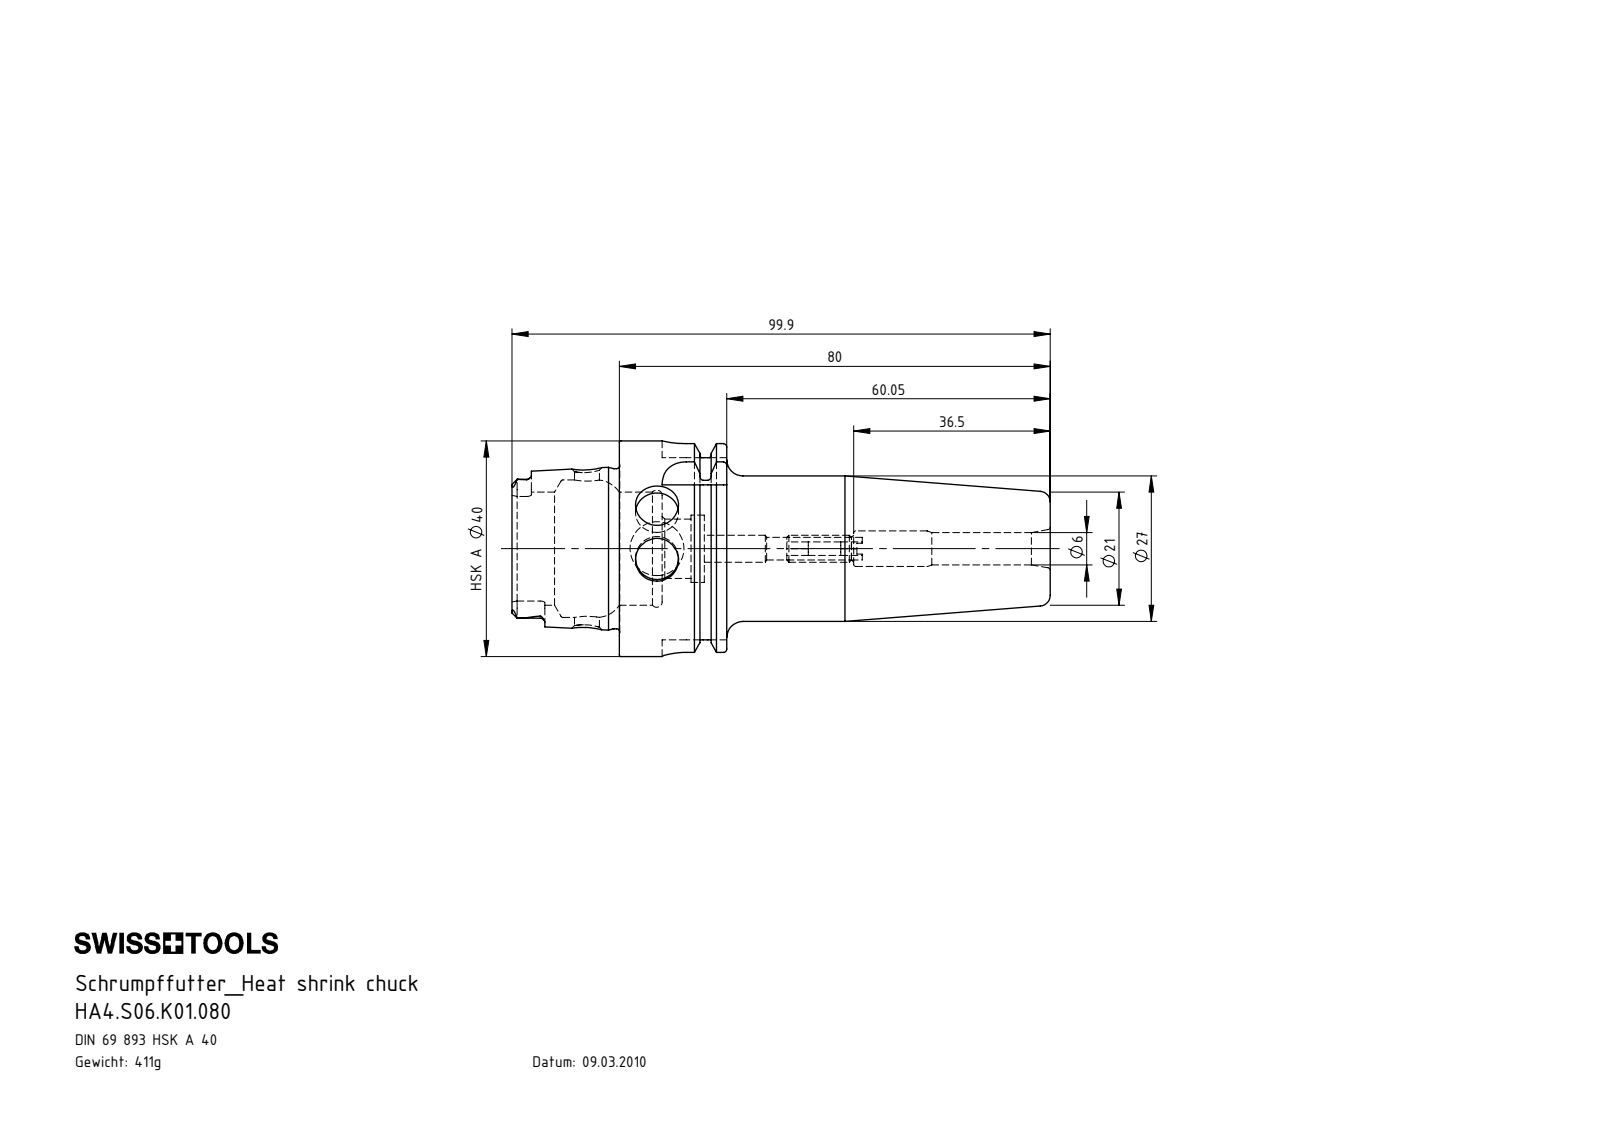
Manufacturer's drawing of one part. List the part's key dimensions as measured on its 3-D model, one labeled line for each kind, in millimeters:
Part name (STEP PRODUCT): HA4-S06.K01.080_C_Fertigbearbeitung; HA4.S06.K01.080; ERU-AN1.K01.014_A
STEP written by: SolidWorks 2017 (CONFIG_CONTROL_DESIGN)
Units: millimetres
Bodies: 2 solids, 230 faces (80 planar, 62 cylindrical, 88 other)
Overall size (bounding box): 99.9 × 40 × 40
Volume: 52 407 mm³ · Surface area: 15 473 mm²
Round holes (diameter × count): ⌀8 ×2, ⌀2.5 ×1, ⌀4.2 ×1, ⌀4.6 ×1, ⌀5 ×1, ⌀6 ×1, ⌀6.6 ×1, ⌀10 ×1, ⌀11 ×1, ⌀12.5 ×1, ⌀21 ×1, ⌀25.5 ×1
Round bosses / shafts (diameter × count): ⌀40 ×1, ⌀34.75 ×1, ⌀29.71 ×1, ⌀27 ×1
Partial cylindrical surfaces — rounded edges, fillets, slot ends (radius × count): R0.9 ×6, R1.88 ×4, R4.5 ×4
Main face-to-face distances: 19.95, 7.95, 12, 80, 72.05, 60.05, 19.9, 27.85, 39.85, 99.9
